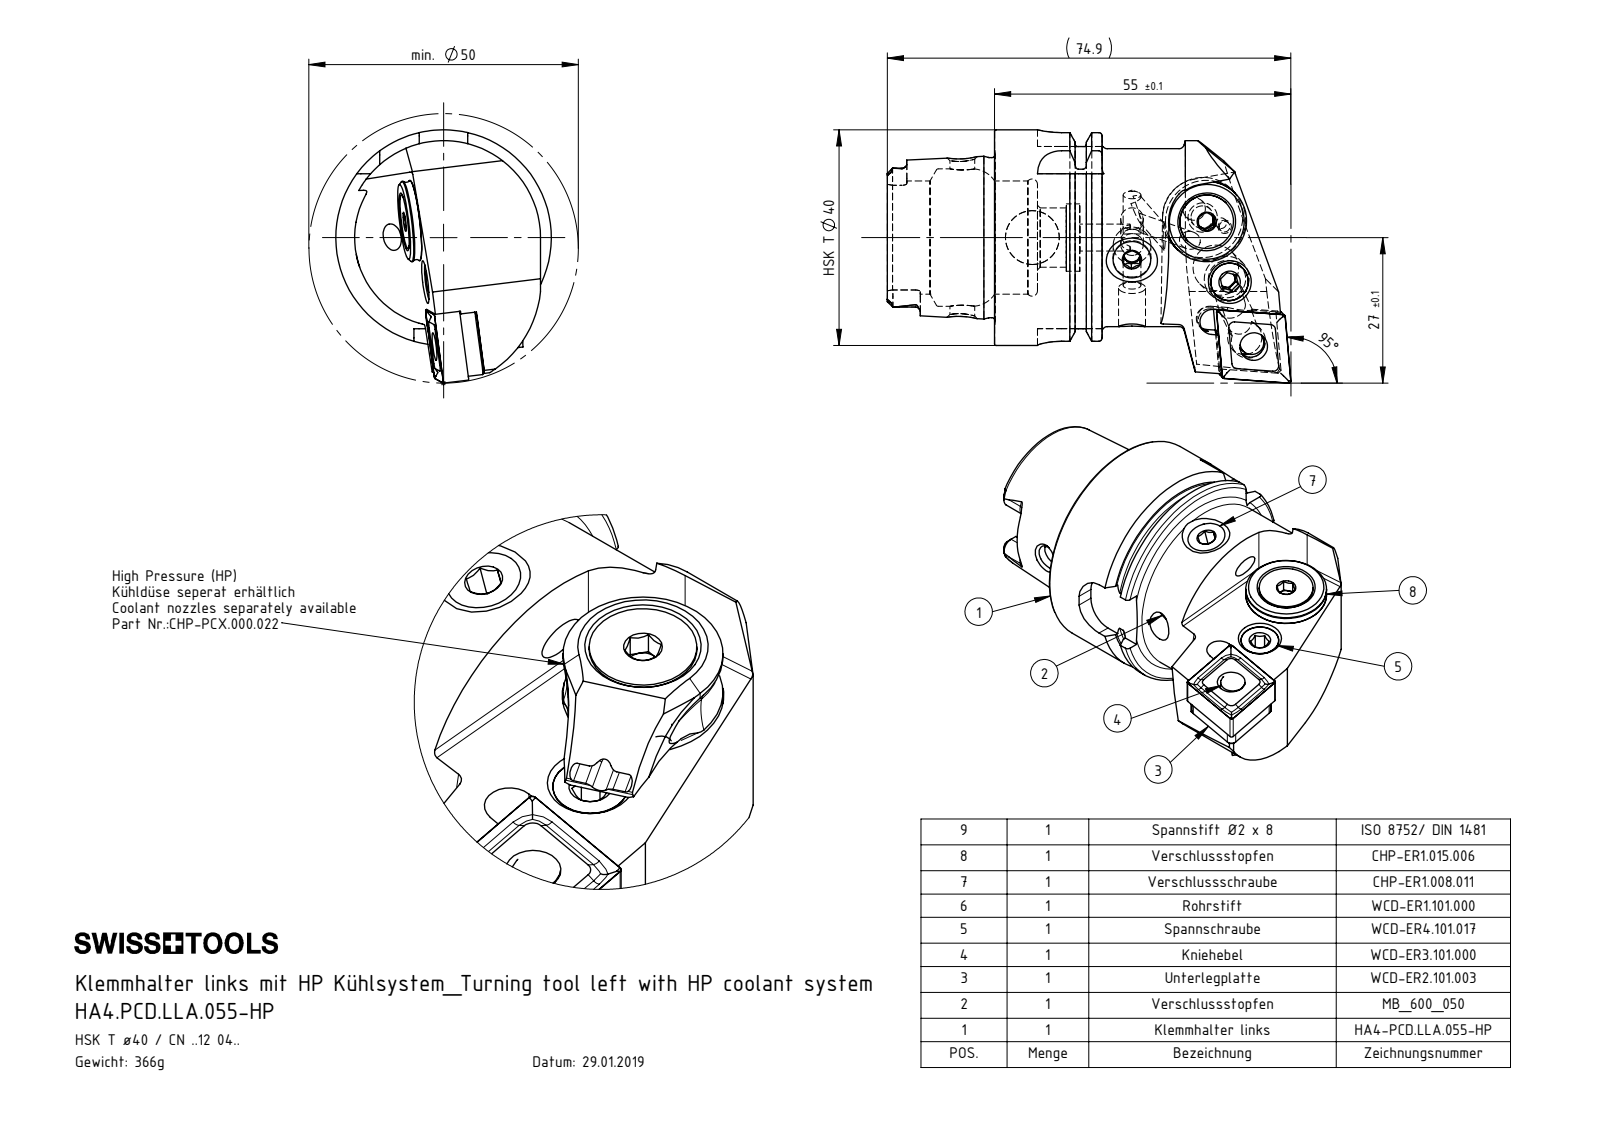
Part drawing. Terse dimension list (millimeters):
name: HA4.PCD.LLA.055-HP; HA4-PCD.LLA.055-HP_A; CHP-ER1.015.006_A; CNMG120404 (+8 more)
written by: SolidWorks 2017 (AUTOMOTIVE_DESIGN)
unit: mm
bodies: 13 solids, 540 faces (167 planar, 148 cylindrical, 225 other)
size: 74.9 × 47 × 40
volume: 46 051 mm³; area: 19 080 mm²
holes: 3× ⌀3.3, 2× ⌀4.2, 2× ⌀5, 2× ⌀7, 1× ⌀1.2, 1× ⌀2, 1× ⌀2.5, 1× ⌀3, 1× ⌀4, 1× ⌀4.6, 1× ⌀5.16, 1× ⌀5.2
bosses: 2× ⌀8, 2× ⌀5, 1× ⌀40, 1× ⌀34.75, 1× ⌀33, 1× ⌀29.71, 1× ⌀15, 1× ⌀13.4
rounds: 6× R0.9, 4× R0.4, 4× R1, 4× R1.88, 4× R4.5, 2× R0.5, 2× R2.5, 1× R2.1
face distances: 4.5, 4.46, 7.95, 19.95, 12, 3.14, 3.18, 7.64, 19.9, 27.85
hole spacings: 4.5, 9.8, 12.45, 22.39, 25.3, 4.49, 12.79, 12.85
